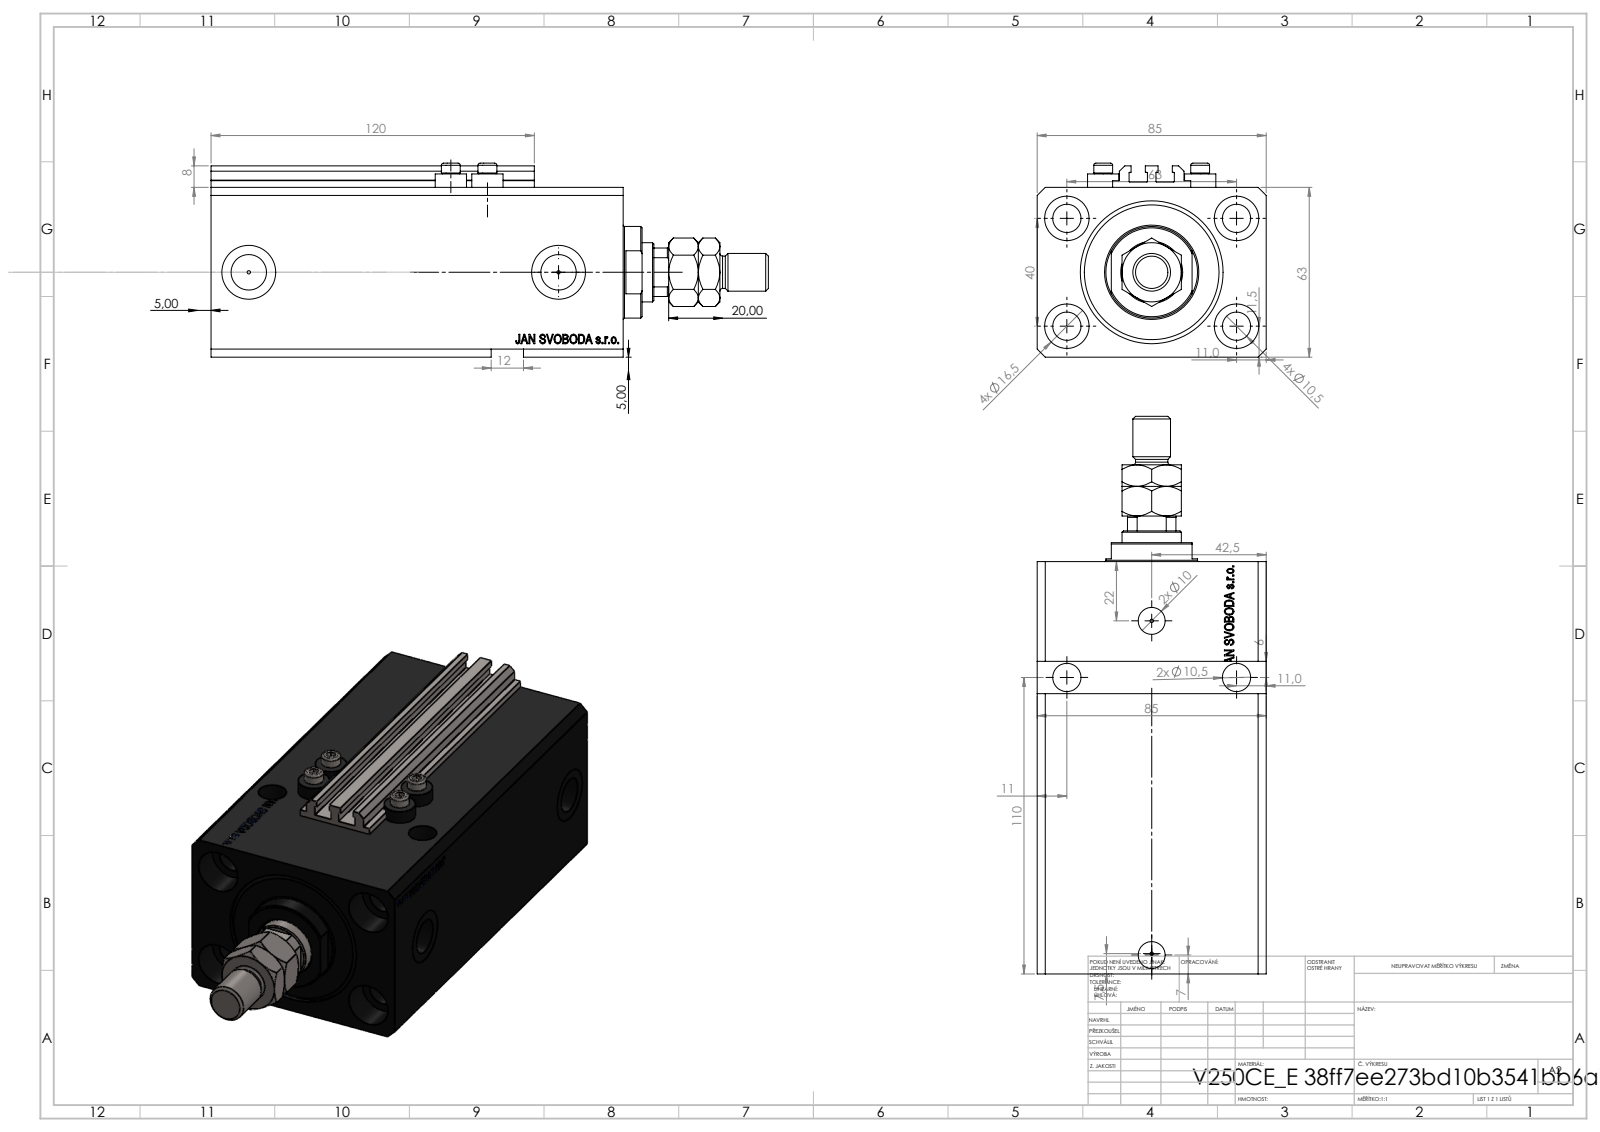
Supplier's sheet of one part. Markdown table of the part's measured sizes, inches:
| quantity | value |
| --- | --- |
| part name | MTA; ALLEN BOLT V250CE; V250CE_E_Body; V250CE_VC_E (+1 more) |
| STEP written by | SolidWorks 2019 (CONFIG_CONTROL_DESIGN) |
| units | inches |
| bodies | 9 solids, 1172 faces (554 planar, 162 cylindrical, 456 other) |
| overall size | 8.15 × 3.346 × 2.835 |
| volume | 42.15 in³ |
| surface area | 224.8 in² |
| round holes (diameter × count) | 0.413 × 8, 0.049 × 4, 0.157 × 4, 0.65 × 4, 0.394 × 2, 0.518 × 2, 0.787 × 2, 0.492 × 1, 0.866 × 1, 1.575 × 1, 2.087 × 1 |
| round bosses / shafts (diameter × count) | 0.457 × 4, 0.276 × 4, 1.339 × 1, 0.551 × 1, 0.472 × 1 |
| partial cylindrical surfaces (radius × count) | 0.008 × 10, 0.413 × 1 |
| main face-to-face distances | 2.48, 3.346, 0.669, 6.024, 5.354, 0.449, 4.906, 5.575, 2.559, 0.394 |
| hole center spacings | 1.469, 2.48, 0.535, 0.606, 0.983, 1.324, 1.417, 1.491 |
